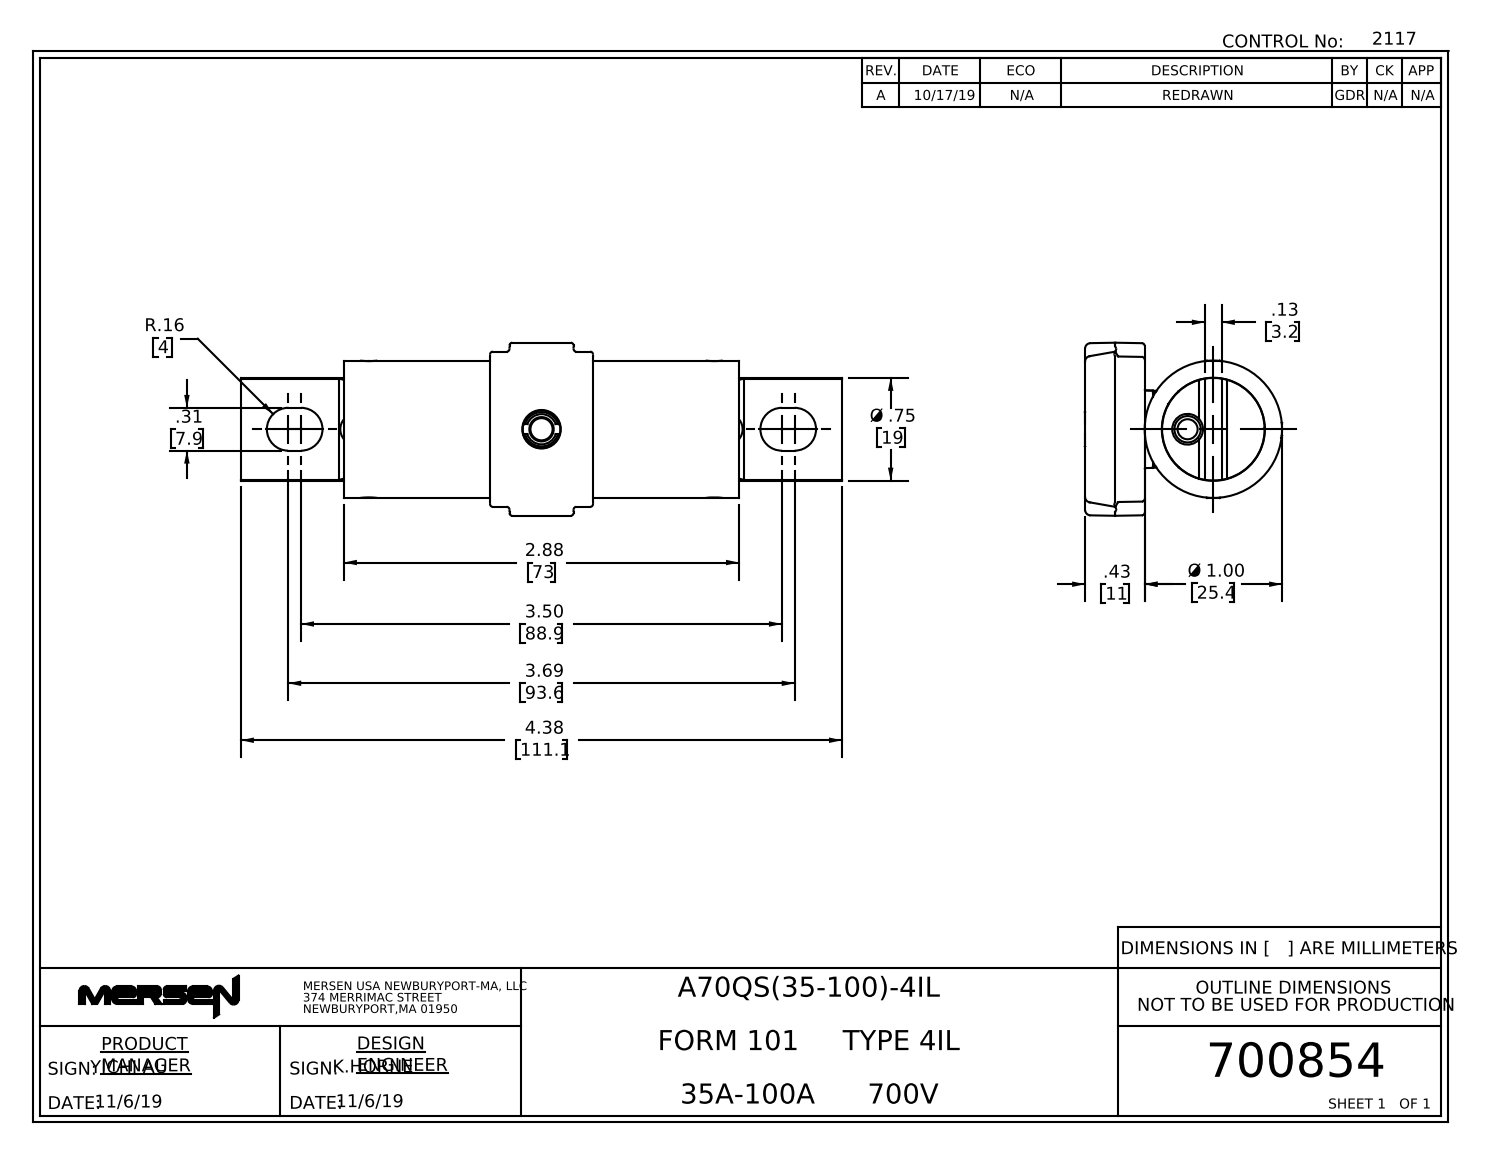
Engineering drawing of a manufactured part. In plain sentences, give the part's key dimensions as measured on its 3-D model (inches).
The part is named "700854revA". Its 3-D file was written by "SolidWorks 2017 (AUTOMOTIVE_DESIGN)". It is 14 solids with 701 faces: 196 planar, 173 cylindrical and 332 other. Overall it measures 4.375 by 1.435 by 1.26 inches. Its volume is 1.603 cubic inches and its surface area 31.53 square inches. Round holes: 4 of diameter 0.125, 1 of diameter 0.146, 1 of diameter 0.177, 1 of diameter 0.187, 1 of diameter 0.299, 1 of diameter 0.609, 1 of diameter 0.75. Round bosses or shafts: 1 of diameter 1, 1 of diameter 0.747, 1 of diameter 0.213, 1 of diameter 0.192, 1 of diameter 0.098. Partial cylindrical surfaces (rounded edges, fillets, slot ends): 42 of radius 0.01, 40 of radius 0.02, 8 of radius 0.04, 4 of radius 0.008, 4 of radius 0.156, 3 of radius 0.01, 1 of radius 0.02, 1 of radius 0.112. The main face-to-face distances are 0.125, 0.332, 2.543, 2.875, 0.75, 0.996, 0.871, 0.067, 2.211, 0.913. The hole center spacings are 2.515, 0.187, 1.257, 1.258.
